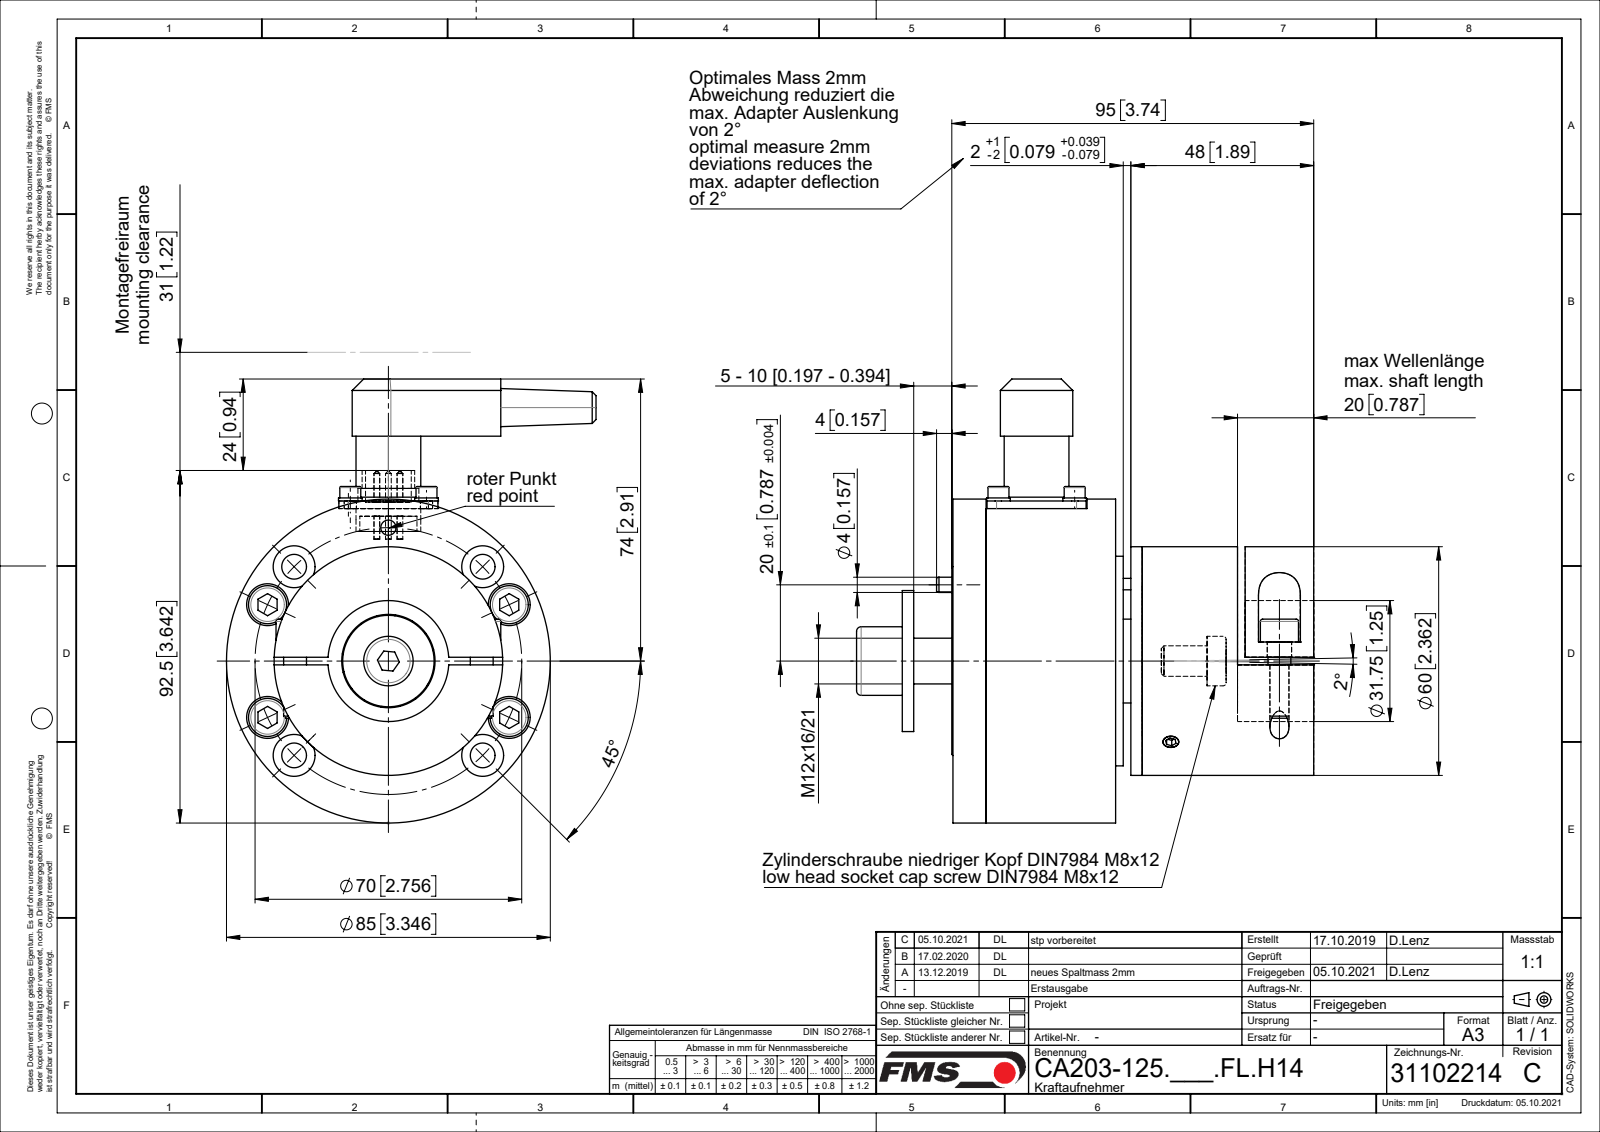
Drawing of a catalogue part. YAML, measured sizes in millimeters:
part_name: "Flanschstecker_M14x1_Mini_5pol; Zyl-Schr DIN912_M6x30; RKL_6203_01; Gew-Sti-I6kt-Zapfen DIN915_M5x10 (+8 more)"
step_written_by: "SolidWorks 2018 (CONFIG_CONTROL_DESIGN)"
units: millimeters
bodies: {solids: 43, faces: 803, planar: 278, cylindrical: 333, other: 192}
overall_size: [120, 116.5, 97]
volume: 309812
surface_area: 113675
round_holes:
  - {diameter: 2.5, count: 8}
  - {diameter: 6.5, count: 8}
  - {diameter: 11, count: 8}
  - {diameter: 5, count: 6}
  - {diameter: 2, count: 5}
  - {diameter: 4, count: 5}
  - {diameter: 3.1, count: 4}
  - {diameter: 3.2, count: 4}
  - {diameter: 3.6, count: 4}
  - {diameter: 7, count: 4}
  - {diameter: 3, count: 2}
  - {diameter: 6.4, count: 2}
round_bosses_or_shafts:
  - {diameter: 3, count: 8}
  - {diameter: 6, count: 7}
  - {diameter: 10, count: 6}
  - {diameter: 1.5, count: 5}
  - {diameter: 6.2, count: 4}
  - {diameter: 5.7, count: 4}
  - {diameter: 5.5, count: 4}
  - {diameter: 85, count: 1}
partial_cylinders:
  - {radius: 2.5, count: 4}
  - {radius: 5, count: 2}
  - {radius: 5.5, count: 2}
  - {radius: 9.5, count: 1}
face_to_face_distances: [2, 41, 45, 10, 30, 3, 60, 34, 50, 22]
hole_center_spacings: [35, 20, 24.78, 25.2, 32.8, 51.14, 56.46, 6]
